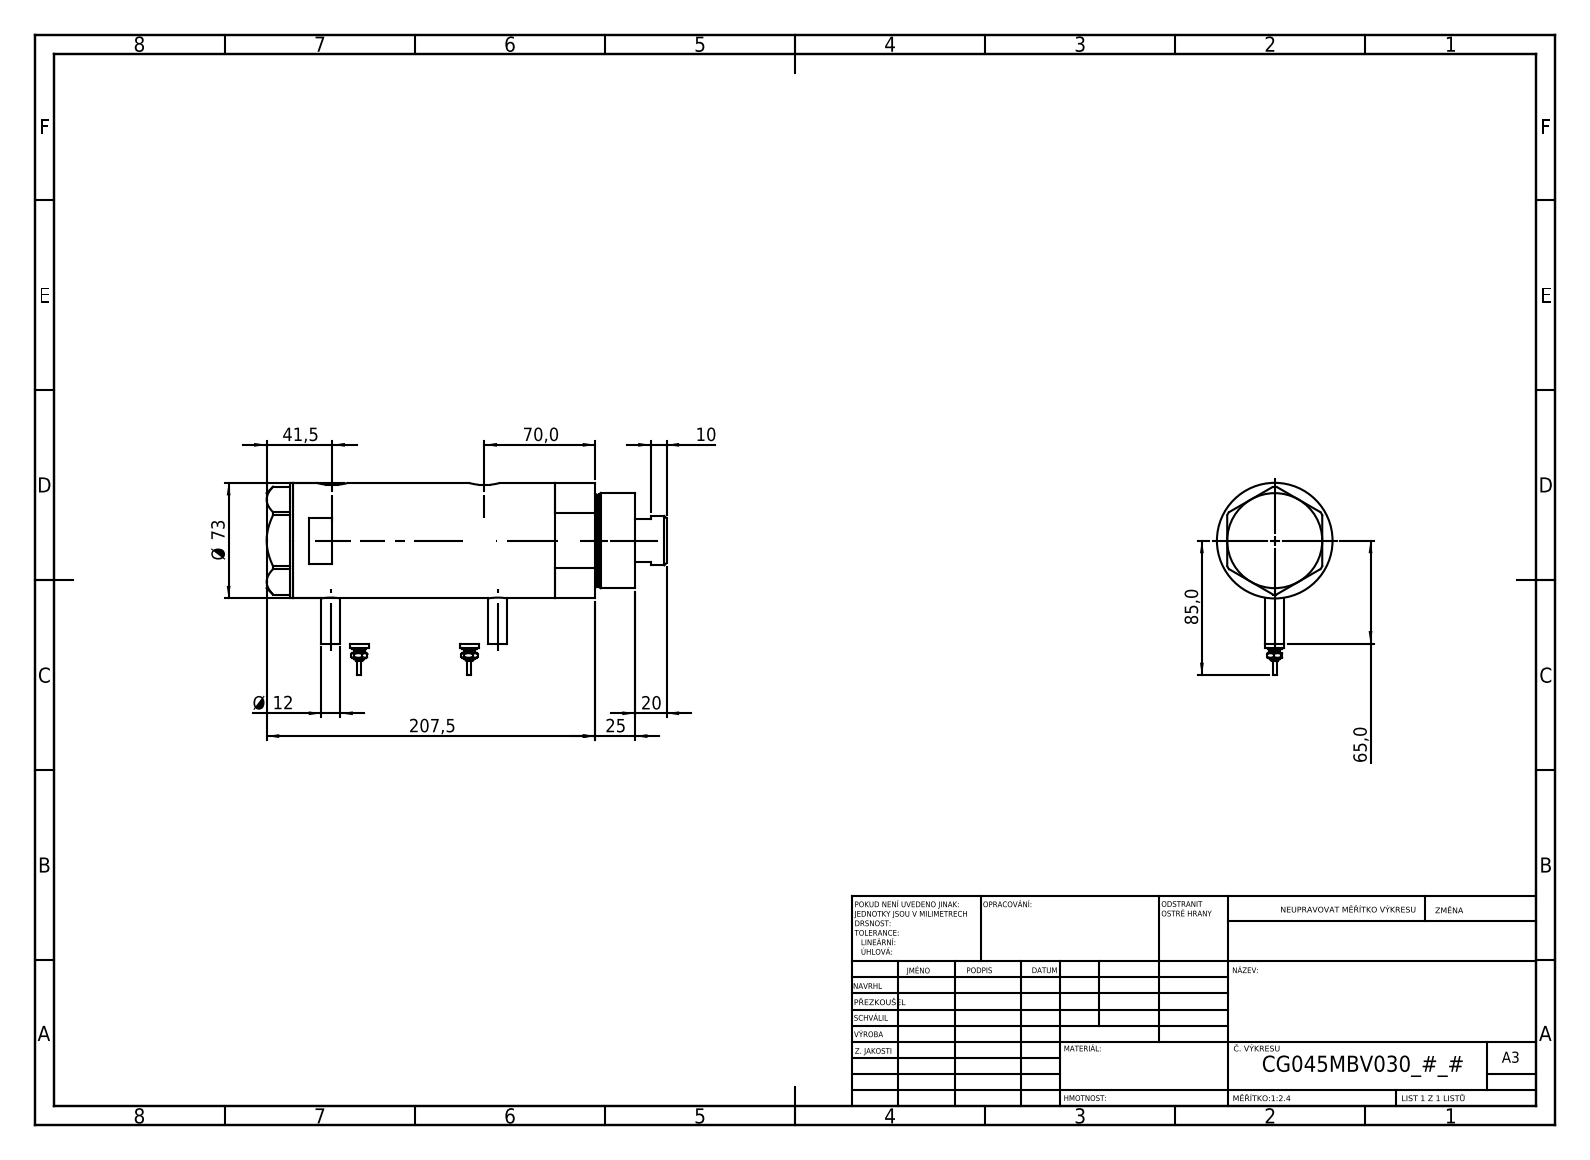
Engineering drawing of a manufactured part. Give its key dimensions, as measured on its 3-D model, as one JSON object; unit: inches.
{"part_name": "V270CG_VC; V270CG_BACK; V270CG_MIDDLE; Switch (+1 more)", "step_written_by": "SolidWorks 2019 (CONFIG_CONTROL_DESIGN)", "units": "inches", "bodies": {"solids": 6, "faces": 212, "planar": 77, "cylindrical": 71, "other": 64}, "overall_size": [9.941, 4.783, 2.874], "volume_in3": 55.4, "surface_area_in2": 236.4, "round_holes": [[0.492, 2], [0.518, 2], [0.413, 1], [1.26, 1], [1.319, 1], [1.772, 1], [1.89, 1], [2.52, 1]], "round_bosses_or_shafts": [[0.472, 4], [0.354, 2], [0.276, 2], [0.177, 2], [0.098, 2], [2.874, 1], [2.362, 1], [2.283, 1]], "partial_cylinders_radius": [[0.394, 2]], "face_to_face_distances": [3.74, 4.764, 1.024, 0.65, 1.673, 5.413, 0.079, 8.504, 9.154, 7.48], "hole_center_spacings": [0.039, 0.335, 3.78, 3.819, 4.114, 4.154]}
